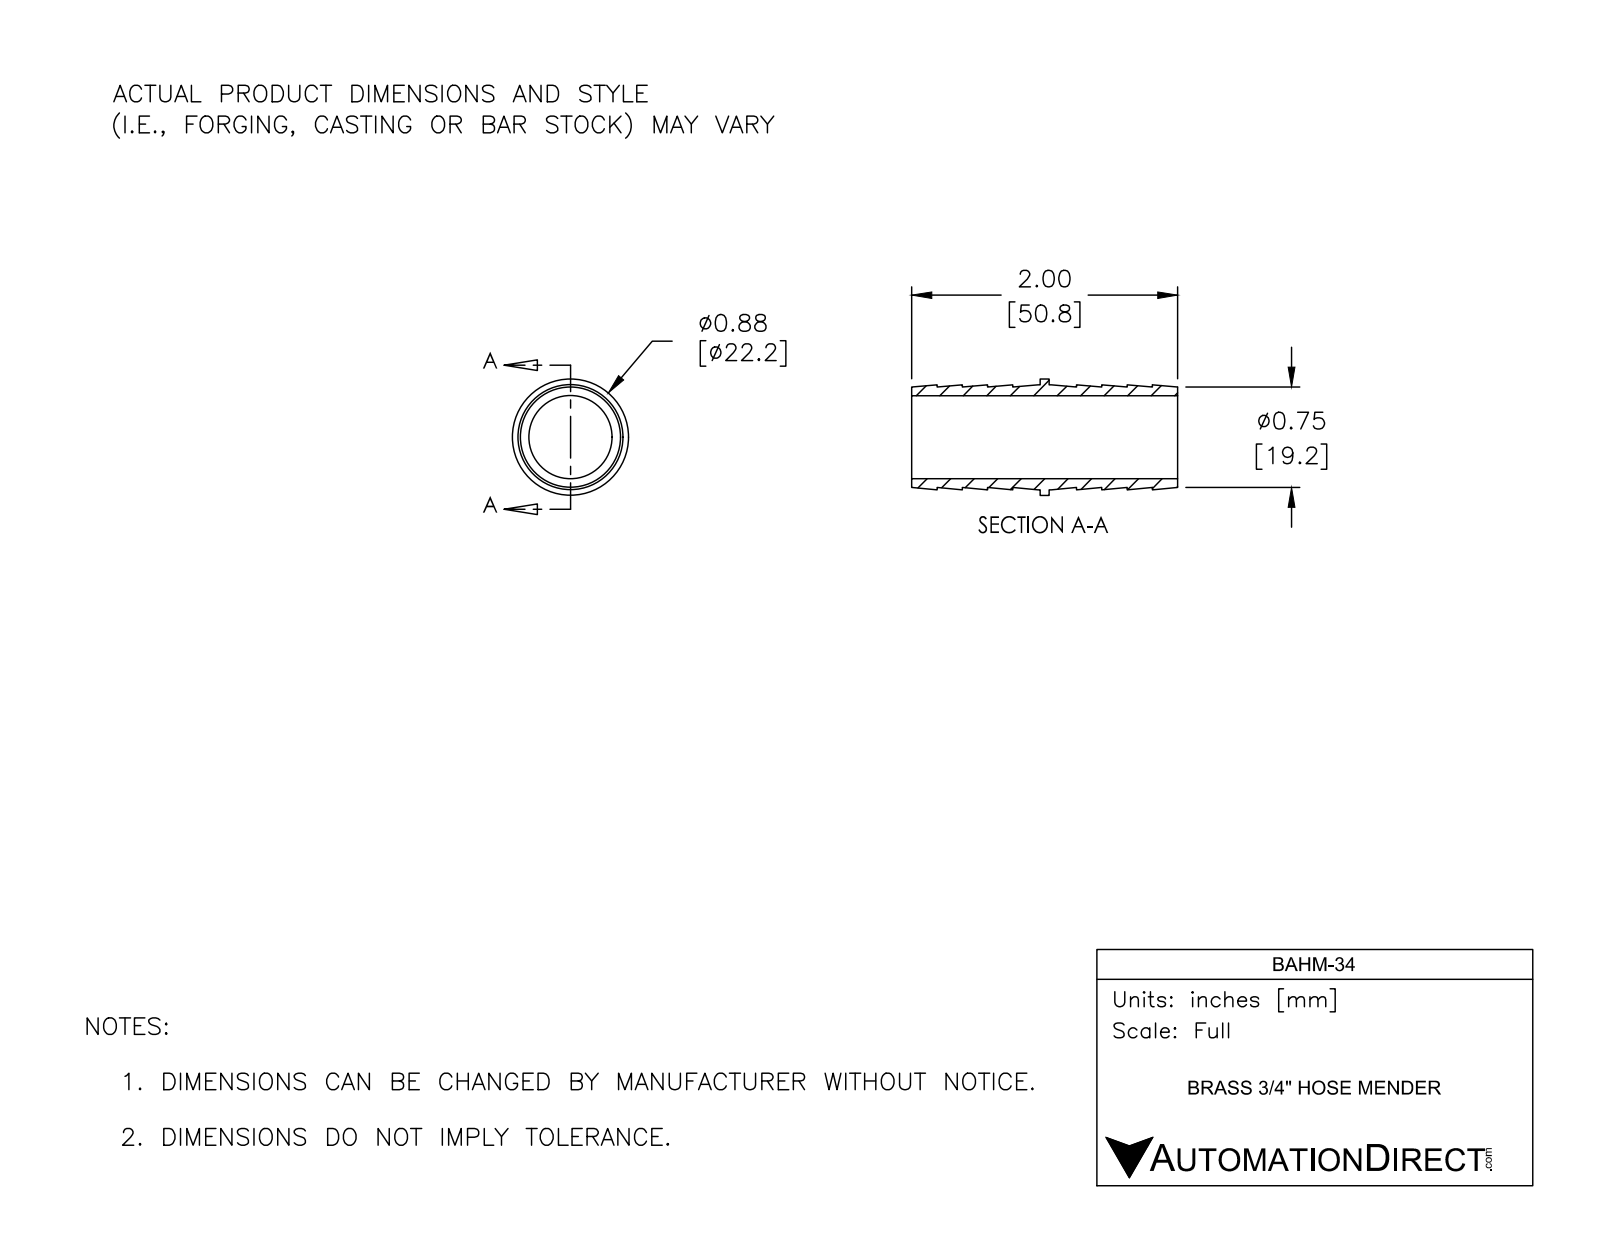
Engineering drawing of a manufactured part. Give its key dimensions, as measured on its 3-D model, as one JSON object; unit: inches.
{"part_name": "BAHM-34", "step_written_by": "SolidWorks 2017 (AUTOMOTIVE_DESIGN)", "units": "inches", "bodies": {"solids": 1, "faces": 40, "planar": 12, "cylindrical": 8, "other": 20}, "overall_size": [2, 0.875, 0.875], "volume_in3": 0.332, "surface_area_in2": 9.673, "round_holes": [[0.625, 1]], "round_bosses_or_shafts": [[0.875, 1], [0.79, 1]], "face_to_face_distances": [0.38, 0.967, 1.033, 0.19, 1.43, 0.19, 1.05, 2, 1.24, 0.067]}
